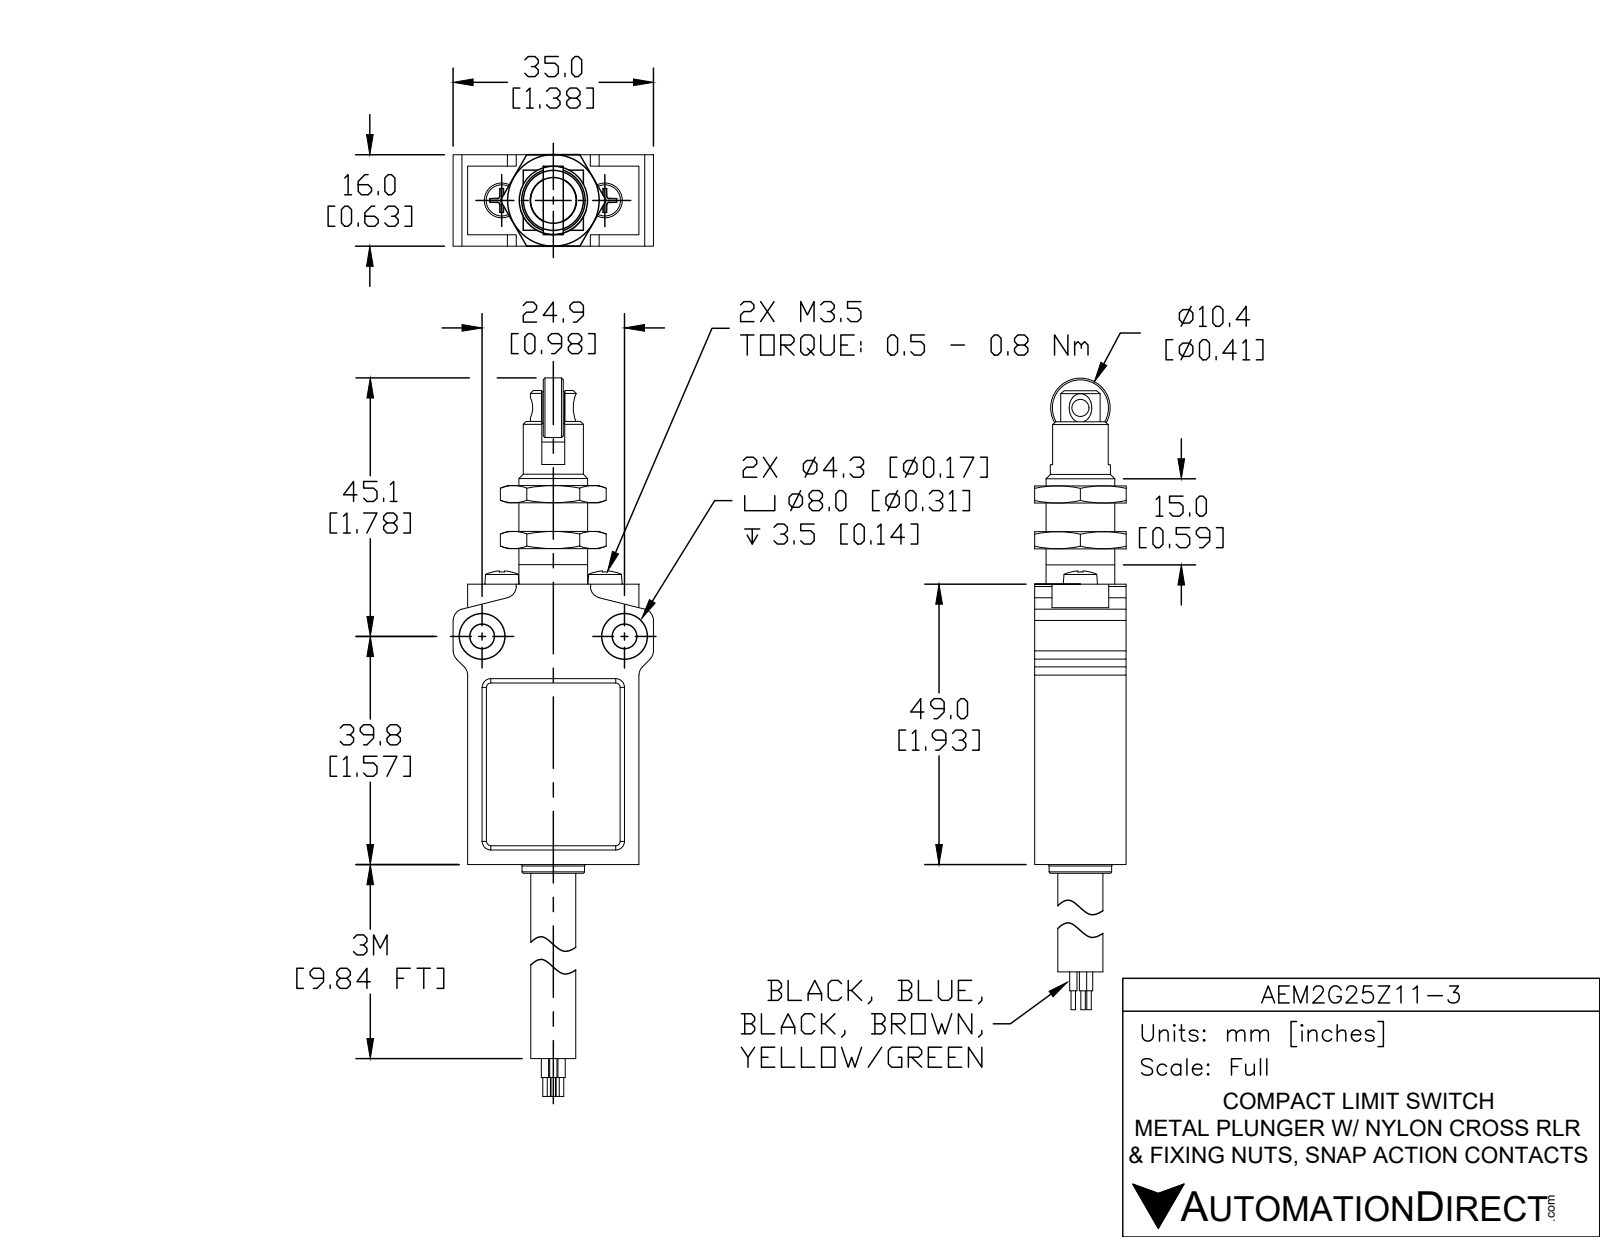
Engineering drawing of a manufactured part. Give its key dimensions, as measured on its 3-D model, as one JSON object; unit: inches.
{"part_name": "AEM2G25Z11-3_Default", "step_written_by": "SolidWorks 2021 (CONFIG_CONTROL_DESIGN)", "units": "inches", "bodies": {"solids": 2, "faces": 191, "planar": 98, "cylindrical": 47, "other": 46}, "overall_size": [3.965, 1.38, 0.63], "volume_in3": 1.565, "surface_area_in2": 14.03, "round_holes": [[0.177, 2], [0.344, 2]], "round_bosses_or_shafts": [[0.05, 5], [0.031, 5], [0.41, 2], [0.47, 1], [0.43, 1], [0.31, 1]], "partial_cylinders_radius": [[0.03, 8], [0.08, 8], [0.135, 1]], "face_to_face_distances": [0.03, 0.6, 0.57, 0.63, 1.18, 0.12, 0.3, 1.93, 0.187, 0.443], "hole_center_spacings": [0.98]}
